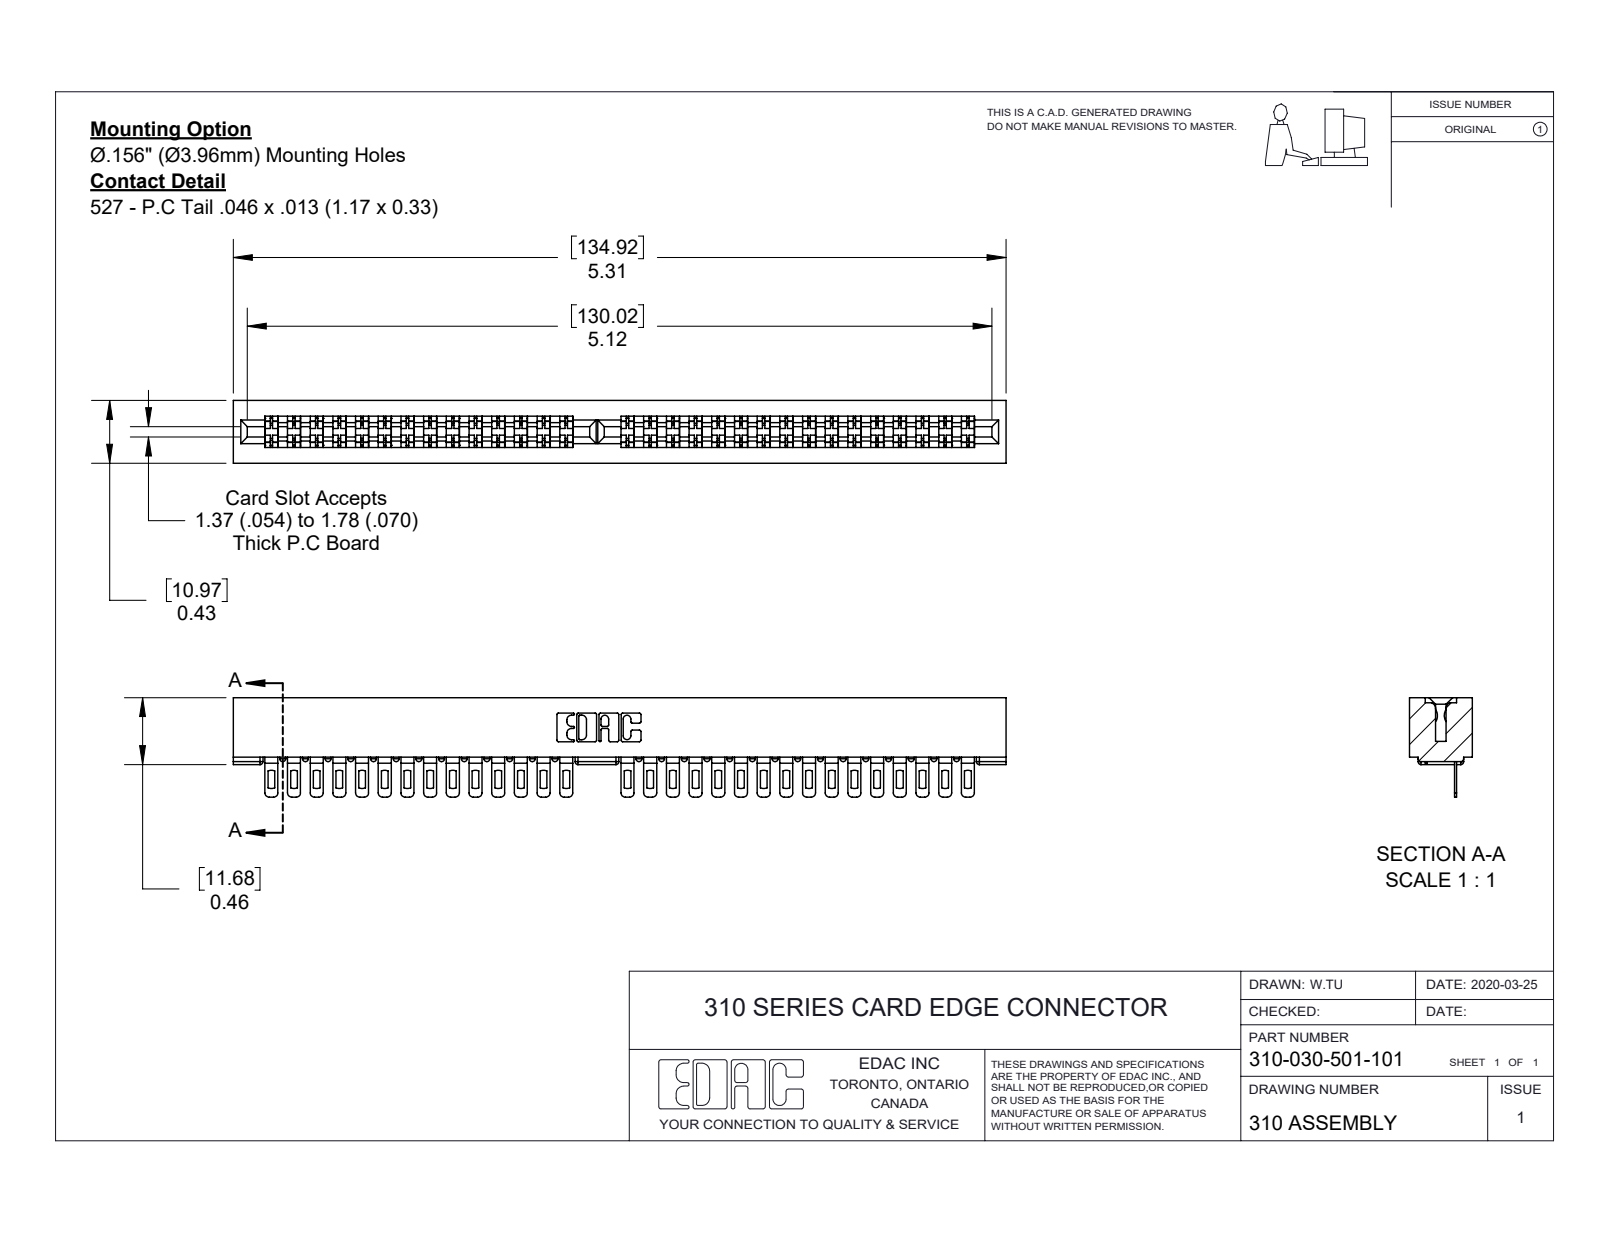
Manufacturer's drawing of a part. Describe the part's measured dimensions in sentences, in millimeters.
The part is named "307-290-002_501; 310 Part_No Mounting Lugs; 310-030-501-101". Its 3-D file was written by "SolidWorks 2016 (CONFIG_CONTROL_DESIGN)". It is 31 solids with 2438 faces: 1400 planar, 974 cylindrical and 64 other. Overall it measures 134.93 by 17.37 by 10.97 millimeters. Its volume is 12 128 cubic millimeters and its surface area 17 643 square millimeters. Partial cylindrical surfaces (rounded edges, fillets, slot ends): 98 of radius 0.51, 60 of radius 0.76, 60 of radius 1.57, 22 of radius 0.25, 6 of radius 0.17, 6 of radius 0.8, 3 of radius 0.67, 2 of radius 0.31. The main face-to-face distances are 2.76, 8.22, 0.33, 3.09, 7.89, 5.13, 5.46, 10.98, 1.24, 3.89.
